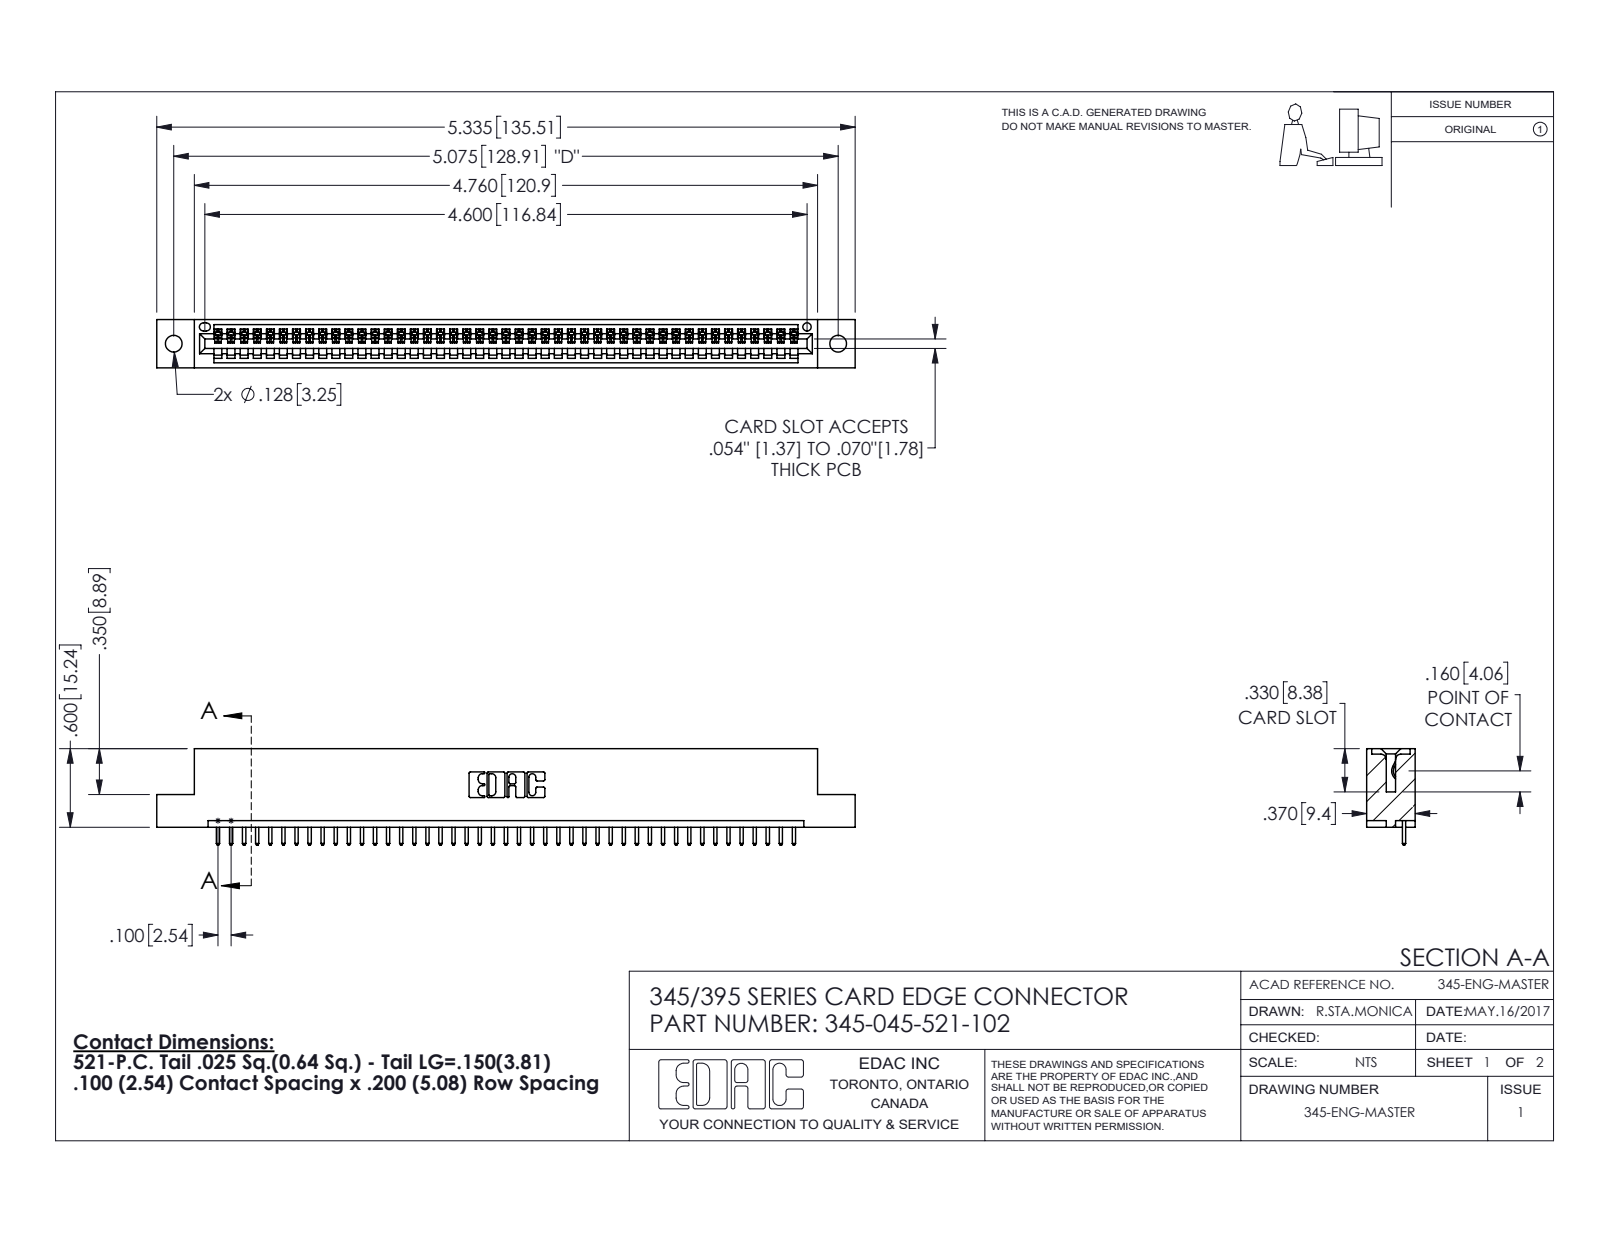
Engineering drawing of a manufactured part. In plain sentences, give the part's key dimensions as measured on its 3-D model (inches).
The part is named "345-045-521-102; 345-292-001_345-293-121; 345 Part_Flush Mounting Lugs - 0.128 Dia". Its 3-D file was written by "SolidWorks 2016 (CONFIG_CONTROL_DESIGN)". It is 46 solids with 2736 faces: 1880 planar, 856 cylindrical and 0 other. Overall it measures 5.335 by 0.737 by 0.37 inches. Its volume is 0.777 cubic inches and its surface area 25.09 square inches. Round holes: 2 of diameter 0.128, 1 of diameter 0.064. Partial cylindrical surfaces (rounded edges, fillets, slot ends): 90 of radius 0.006, 90 of radius 0.01, 22 of radius 0.01, 6 of radius 0.007, 6 of radius 0.031, 3 of radius 0.026, 2 of radius 0.031, 2 of radius 0.04. The main face-to-face distances are 0.298, 0.072, 0.37, 0.2, 0.098, 0.272, 0.025, 0.225, 0.149, 0.072. The hole center spacings are 0.27, 4.839, 5.075.
